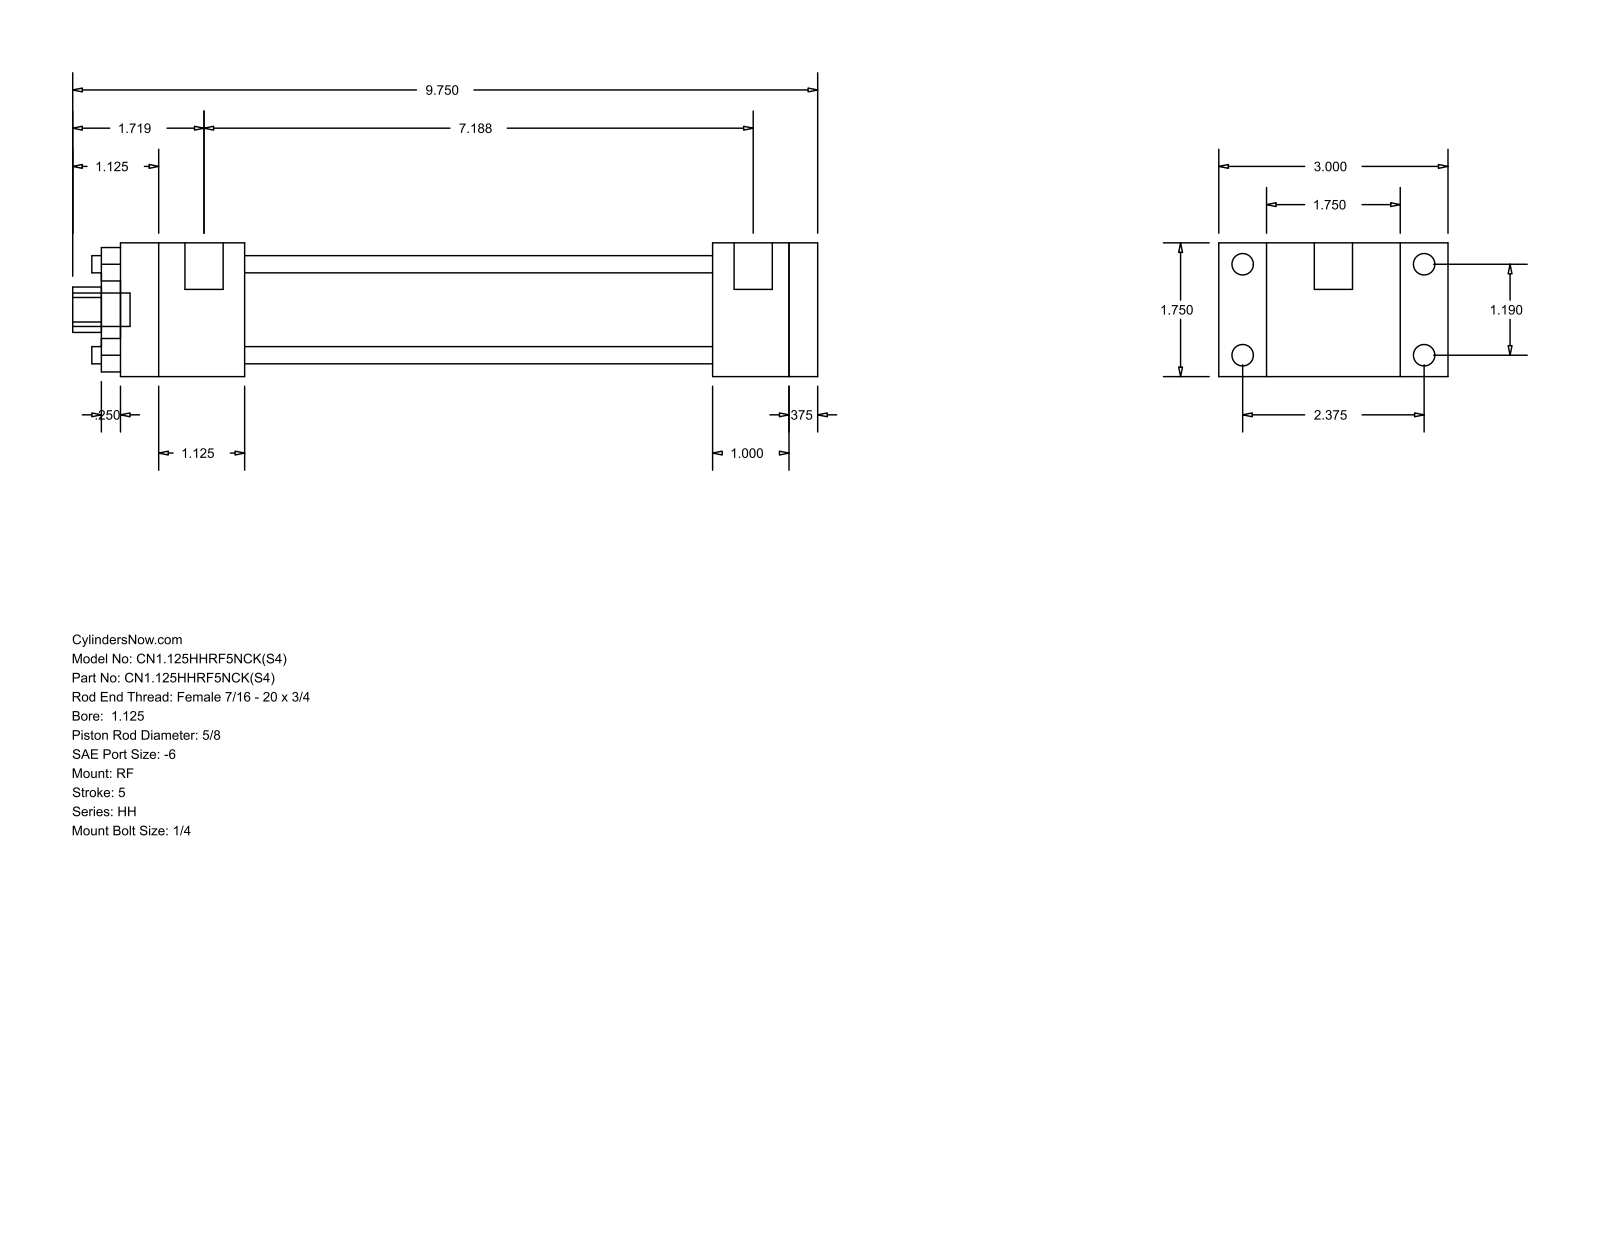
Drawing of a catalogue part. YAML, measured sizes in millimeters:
part_name: "HH_RF__0112_0.625"
step_written_by: "GSSL Pune (CONFIG_CONTROL_DESIGN)"
units: millimeters
bodies: {solids: 0, faces: 92, planar: 64, cylindrical: 28, other: 0}
overall_size: [247.65, 76.2, 44.45]
round_holes:
  - {diameter: 5.71, count: 4}
  - {diameter: 15.88, count: 1}
  - {diameter: 28.57, count: 1}
  - {diameter: 34.92, count: 1}
round_bosses_or_shafts:
  - {diameter: 7.14, count: 4}
  - {diameter: 5.56, count: 4}
  - {diameter: 12.7, count: 2}
  - {diameter: 11.11, count: 1}
partial_cylinders:
  - {radius: 7.54, count: 1}
face_to_face_distances: [44.46, 9.53, 231.77, 15.87, 180.97, 190.5, 155.57, 25.4, 34.93, 41.27]
hole_center_spacings: [21.37, 30.22, 42.74]
